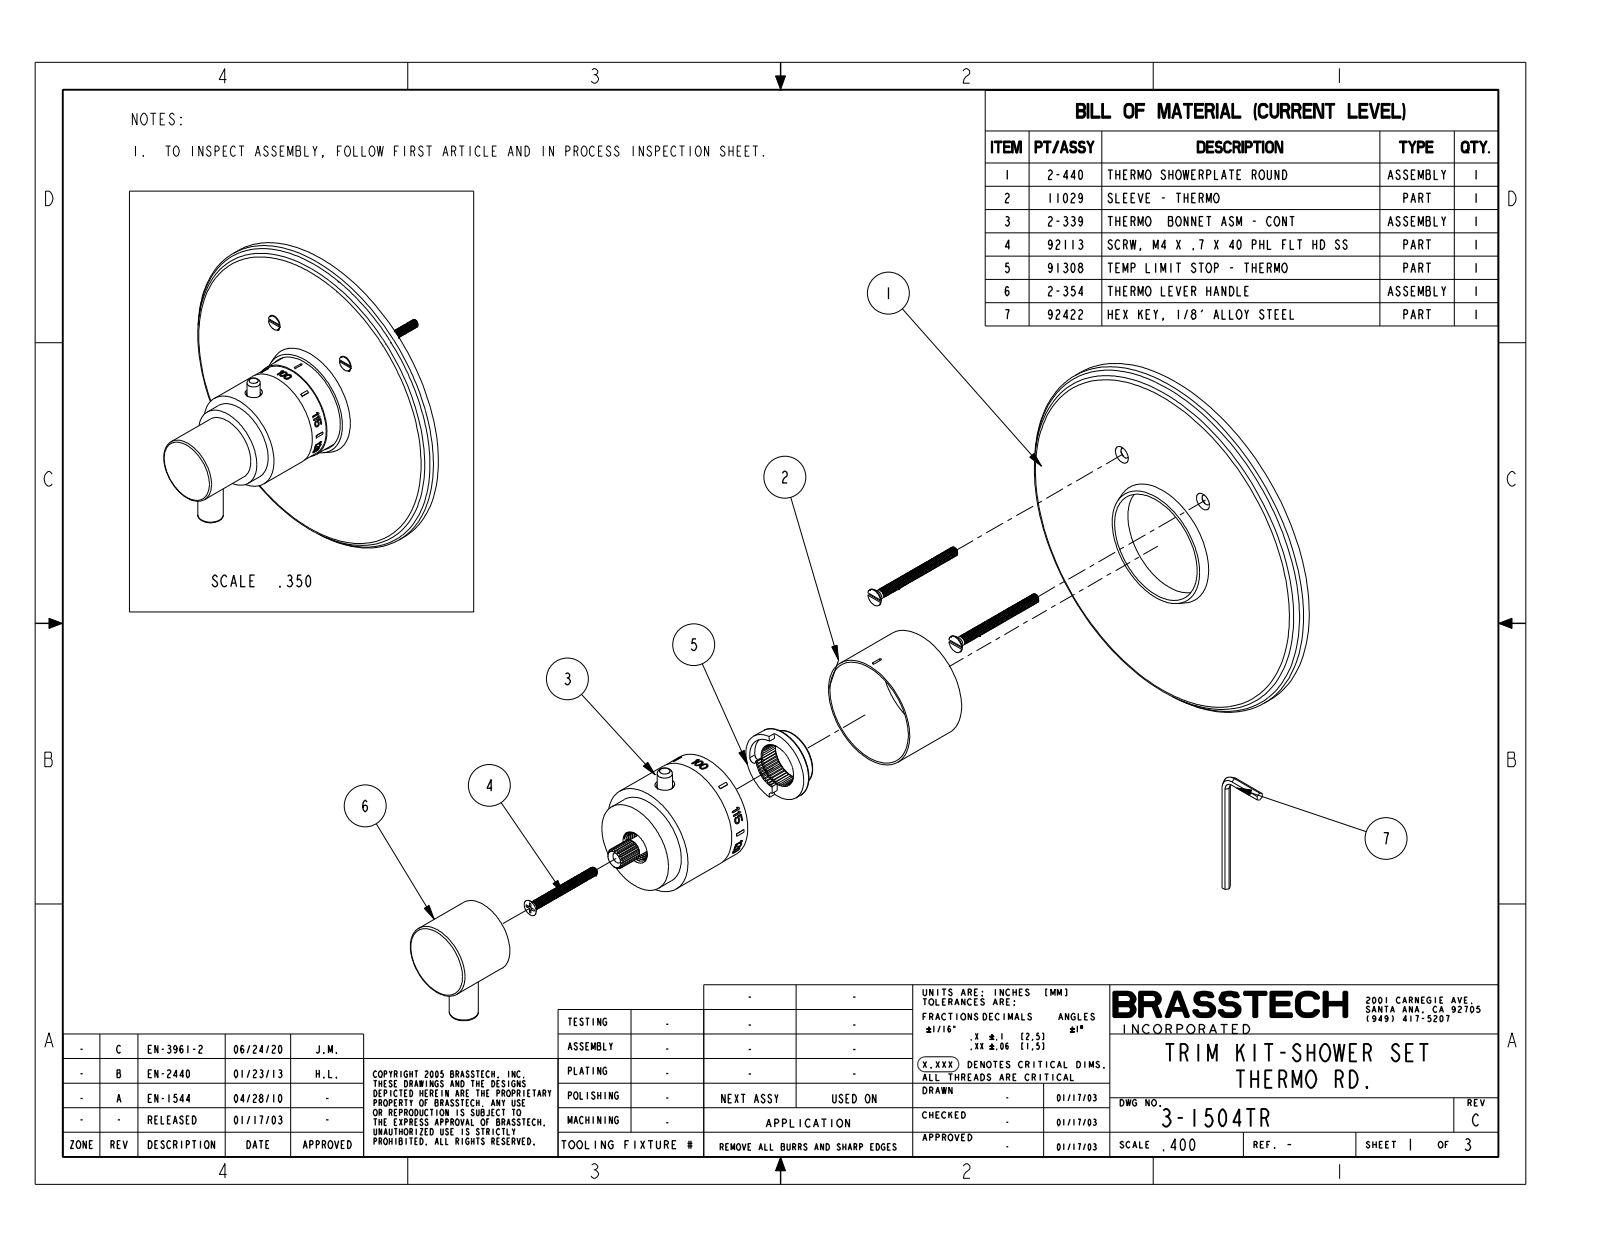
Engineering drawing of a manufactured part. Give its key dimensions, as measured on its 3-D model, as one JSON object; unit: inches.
{"part_name": "3-1504TR", "step_written_by": "CREO PARAMETRIC BY PTC INC, 2018400 (CONFIG_CONTROL_DESIGN)", "units": "inches", "bodies": {"solids": 1, "faces": 408, "planar": 331, "cylindrical": 49, "other": 28}, "overall_size": [6.5, 6.5, 3.729], "volume_in3": 18.41, "surface_area_in2": 93.33, "round_holes": [[0.196, 1], [0.25, 1]], "round_bosses_or_shafts": [[6.5, 1], [1.97, 1], [1.94, 1], [1.929, 1], [1.615, 1], [1.312, 1], [0.5, 1], [0.4, 1]], "partial_cylinders_radius": [[0.969, 1]], "face_to_face_distances": [0.313, 2.593, 2.28, 3.73, 3.417, 1.136, 0.016, 2.609, 2.296, 1.12]}
